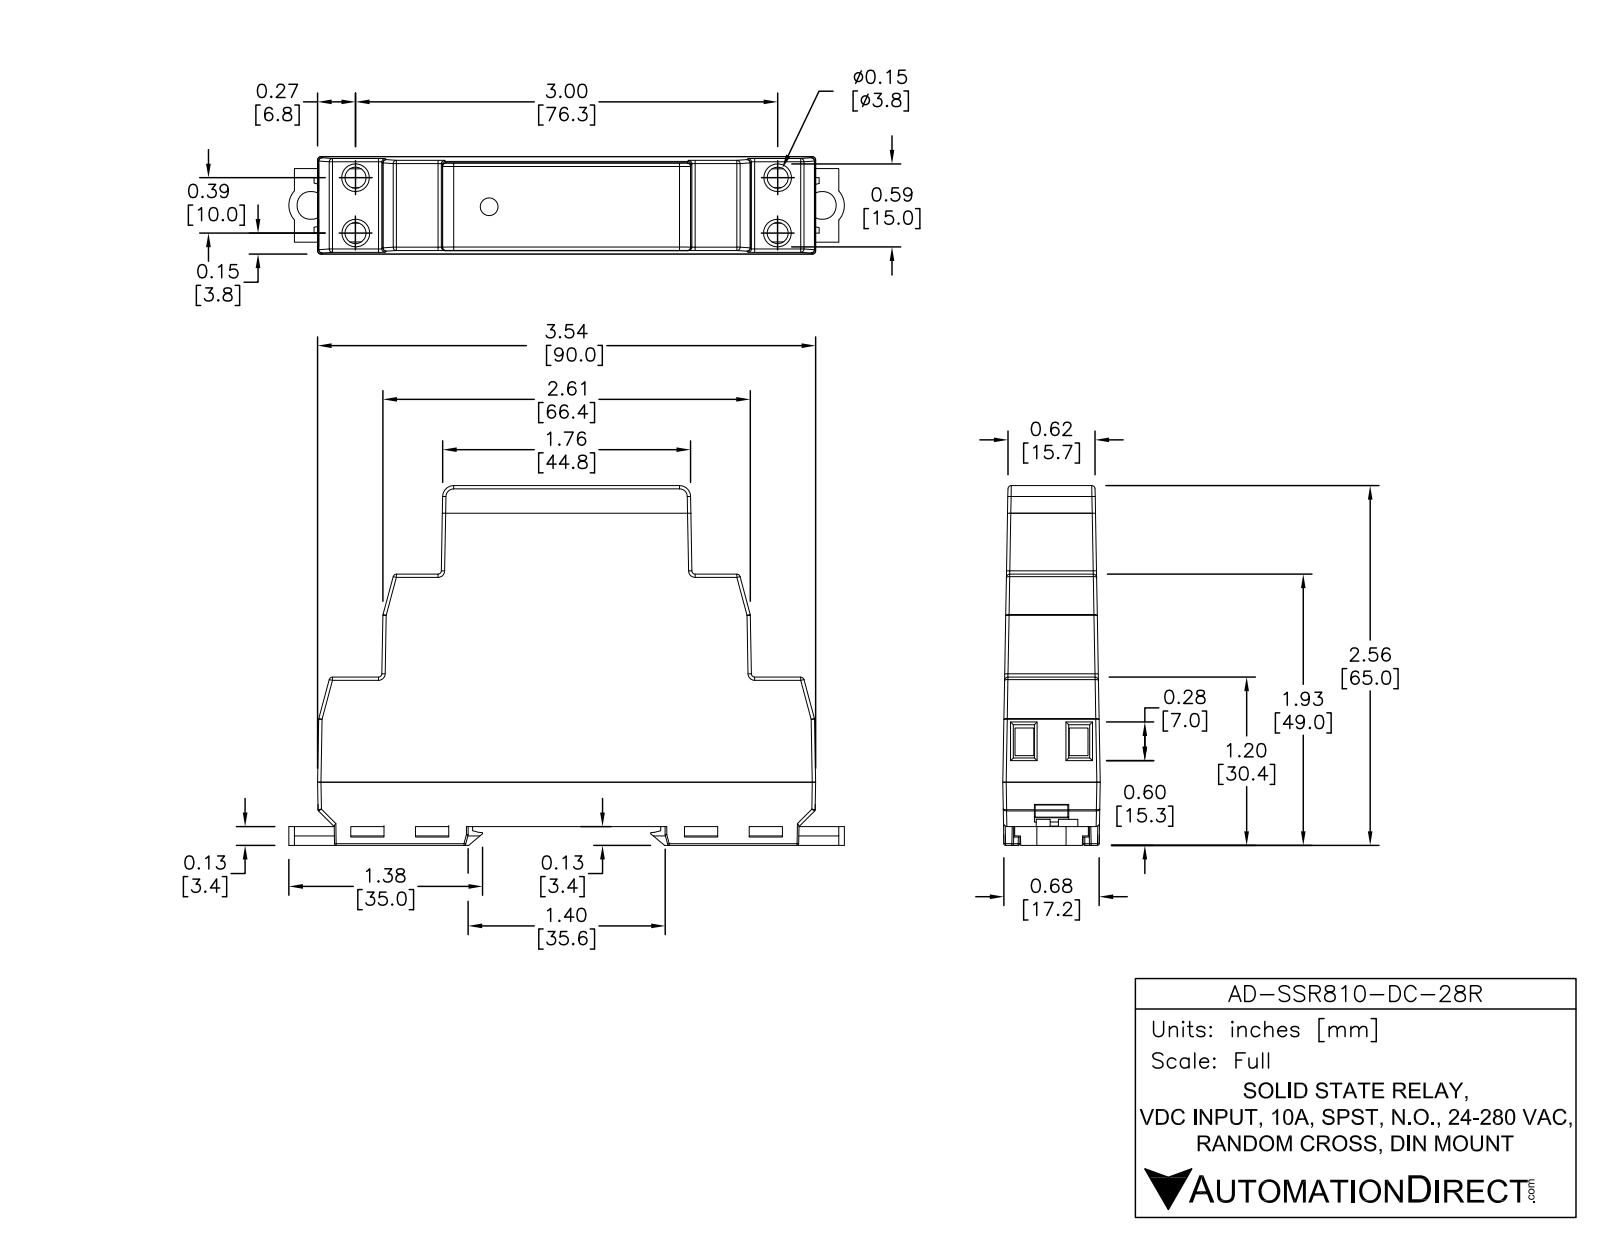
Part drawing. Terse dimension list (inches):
name: AD-SSR810-DC-28R
written by: SolidWorks 2013 (AUTOMOTIVE_DESIGN)
unit: in
bodies: 1 solid, 844 faces (490 planar, 78 cylindrical, 276 other)
size: 3.924 × 2.616 × 0.685
volume: 4.605 in³; area: 24.23 in²
holes: 4× ⌀0.19, 2× ⌀0.2
bosses: 1× ⌀0.105
rounds: 41× R0.015, 2× R0.06, 2× R0.172
face distances: 2.525, 0.049, 2.574, 0.425, 2.215, 0.025, 0.05, 1.934, 1.885, 0.64
hole spacings: 0.338, 3.3, 0.364, 3.01, 3.032, 3.58
